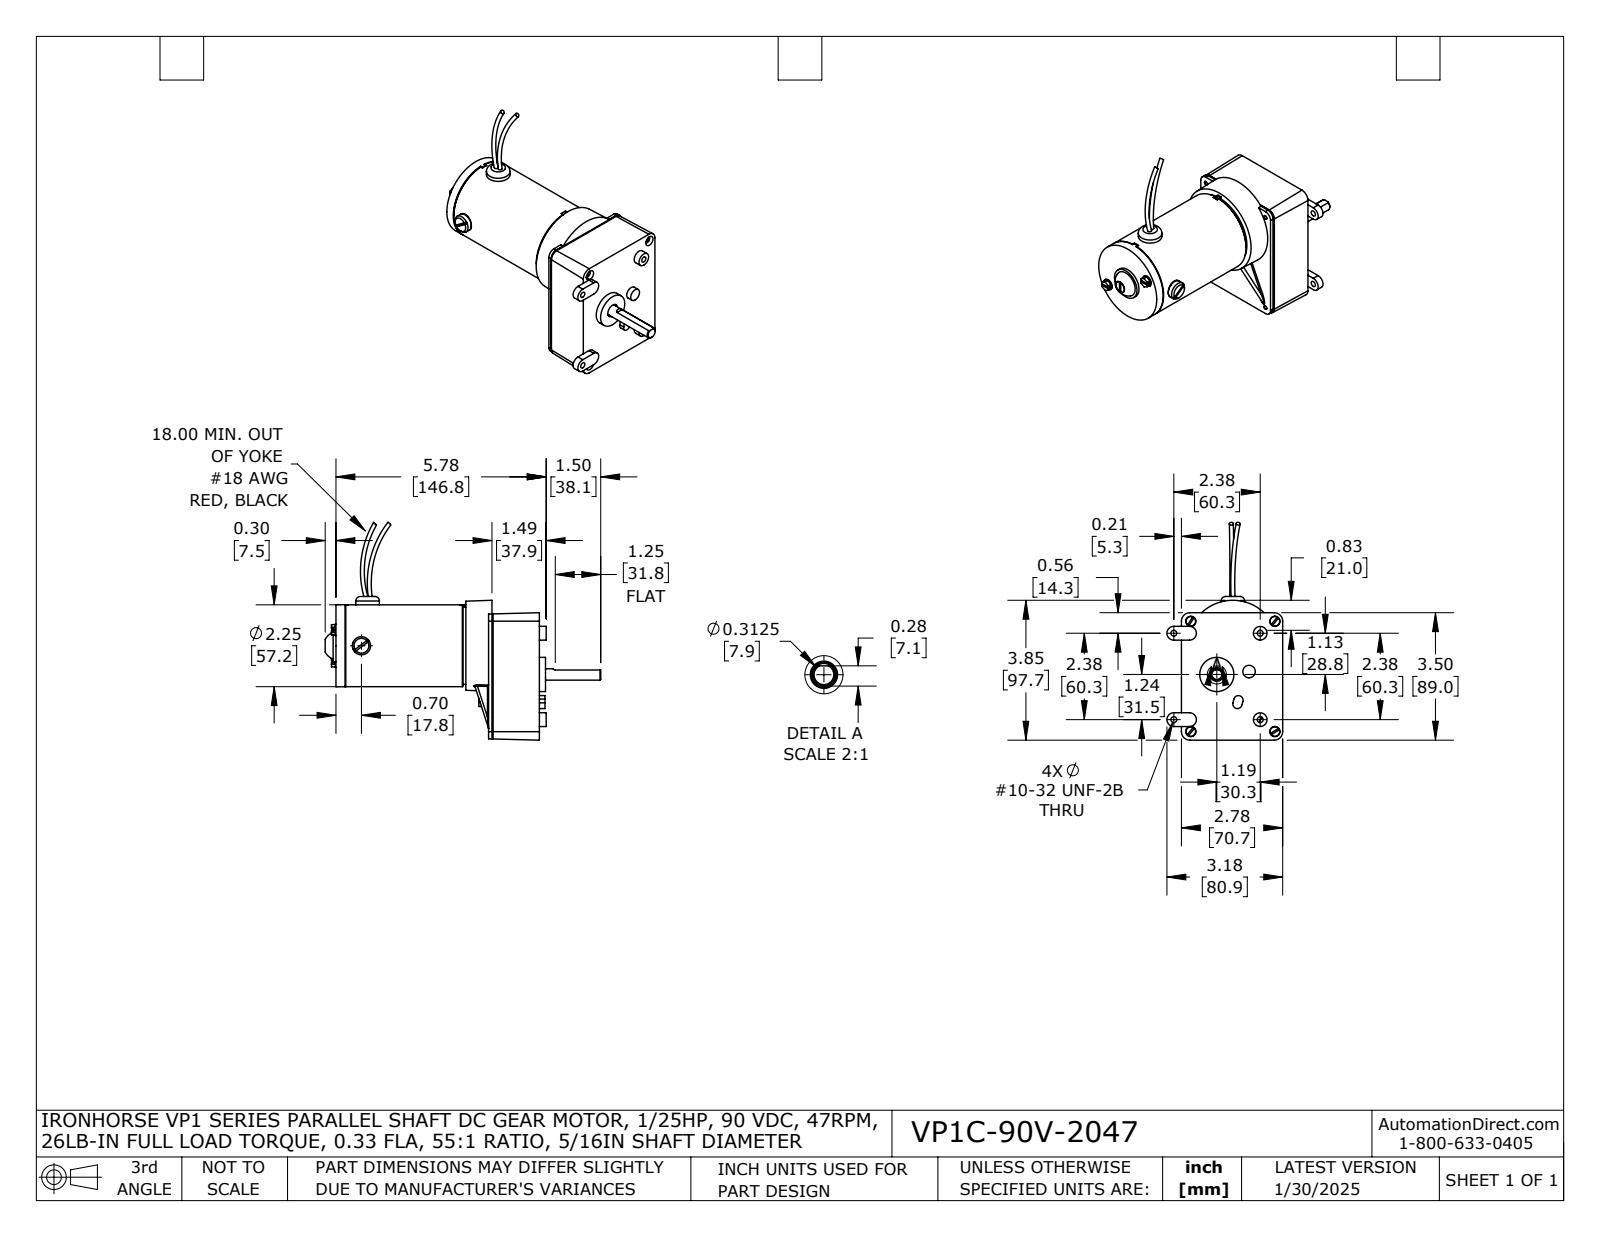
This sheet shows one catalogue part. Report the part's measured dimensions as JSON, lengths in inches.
{"part_name": "VP1C-90V-2047", "step_written_by": "SolidWorks 2021 (AUTOMOTIVE_DESIGN)", "units": "inches", "bodies": {"solids": 34, "faces": 1338, "planar": 477, "cylindrical": 580, "other": 281}, "overall_size": [7.578, 5.989, 3.183], "volume_in3": 13.71, "surface_area_in2": 226.6, "round_holes": [[0.281, 7], [0.037, 4], [0.117, 4], [0.149, 4], [0.15, 4], [0.161, 4], [0.125, 2], [0.187, 2], [0.127, 1], [0.127, 1], [0.213, 1], [0.239, 1]], "round_bosses_or_shafts": [[0.136, 4], [0.313, 3], [0.375, 2], [2.256, 1], [2.25, 1], [2.123, 1], [2.003, 1], [2, 1]], "partial_cylinders_radius": [[0.028, 24], [0.051, 24], [0.02, 12], [0.055, 12], [0.058, 12], [0.03, 8], [0.031, 8], [0.19, 8]], "face_to_face_distances": [1.304, 0.097, 1.207, 1.397, 1.3, 0.093, 1.273, 1.176, 0.031, 0.124], "hole_center_spacings": [0.875, 0.77, 1.936, 2.31, 2.312, 3.03, 3.031, 0.135]}
